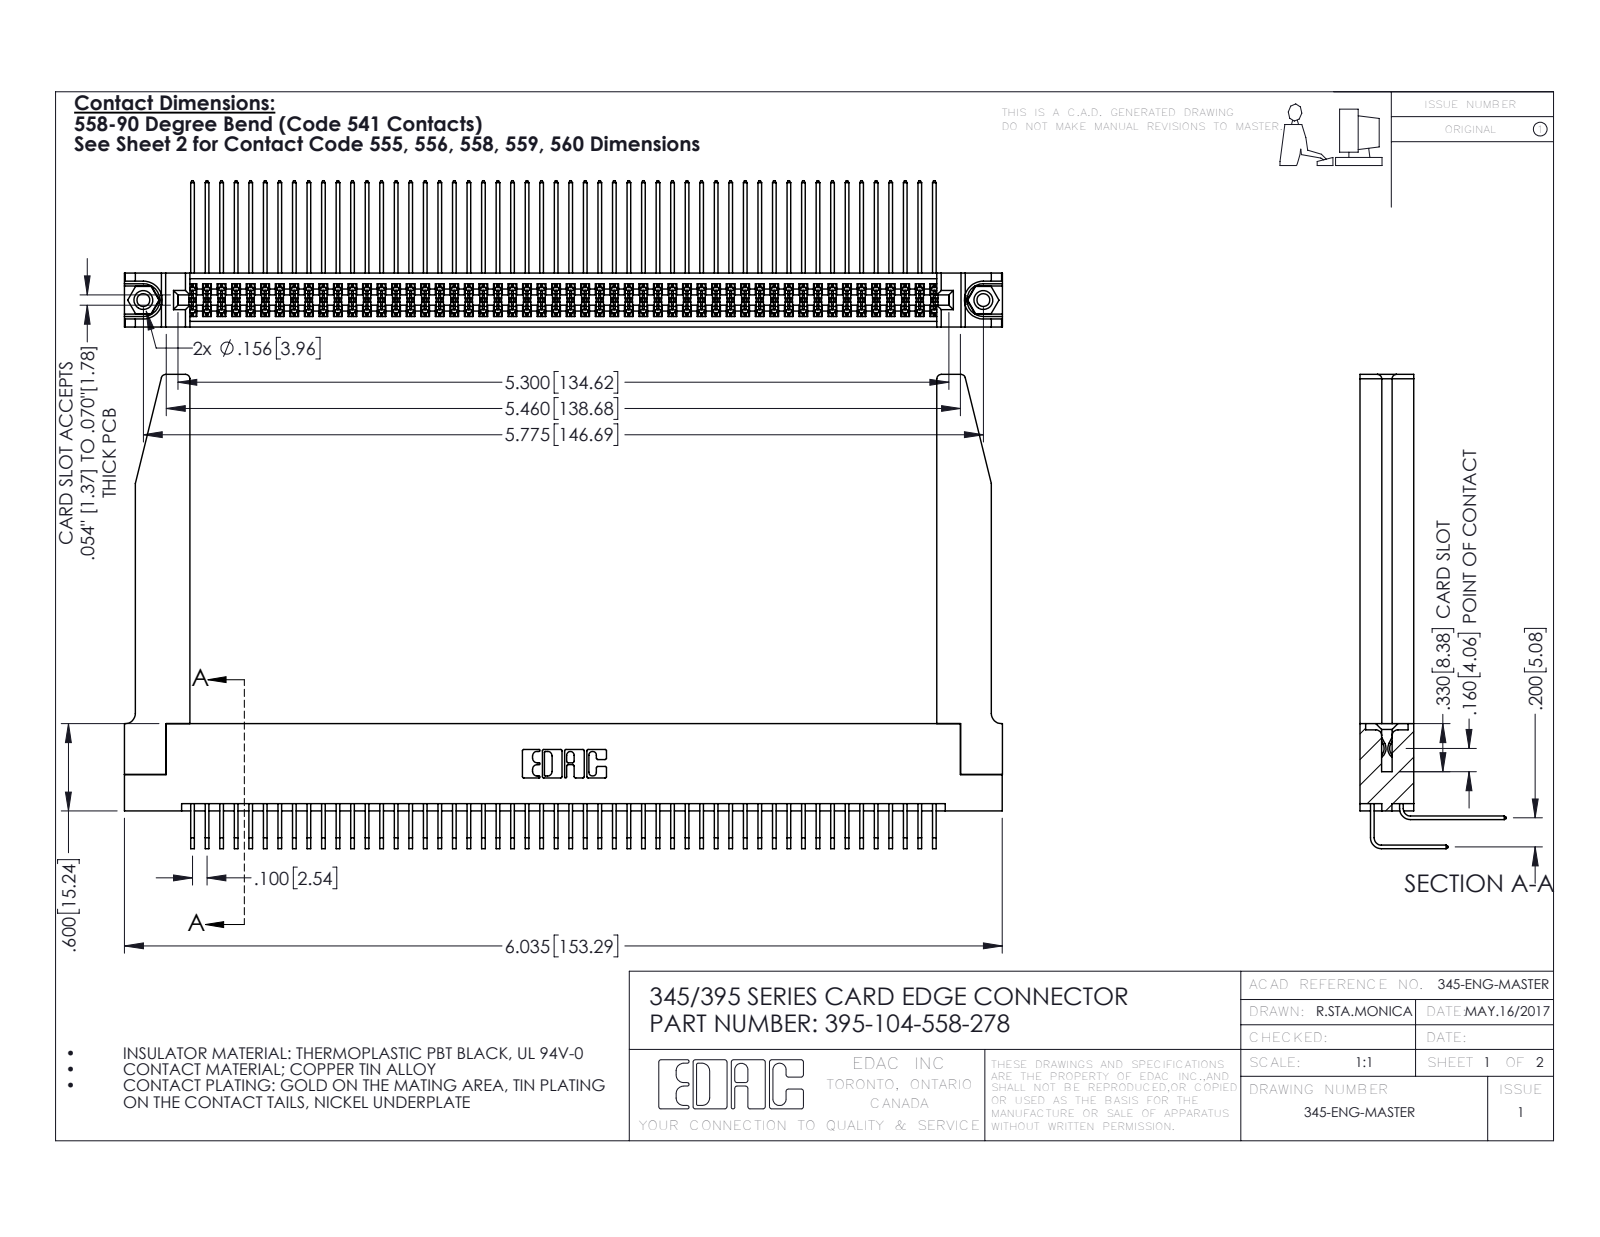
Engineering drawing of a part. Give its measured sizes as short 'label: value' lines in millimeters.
name: 345-292-001_558 559 Tail - 1; 395-104-558-278; 345-250-001_345-250-001-102; 345-220-078_345-220-078 (+2 more)
written by: SolidWorks 2016 (CONFIG_CONTROL_DESIGN)
unit: mm
bodies: 109 solids, 5768 faces (3862 planar, 1854 cylindrical, 52 other)
size: 153.3 × 82.8 × 25.5
volume: 23 350 mm³; area: 32 890 mm²
holes: 2× ⌀2.3, 2× ⌀3.2, 2× ⌀4, 1× ⌀1.6
bosses: 2× ⌀3.9
rounds: 157× R0.2, 22× R0.3, 8× R0.8, 6× R0.2, 6× R0.8, 3× R0.7, 2× R0.4, 2× R0.5
face distances: 1.8, 7.6, 9.4, 5.1, 2.5, 6.9, 0.6, 5.7, 7.2, 0.6
hole spacings: 6.9, 140.7, 146.7
